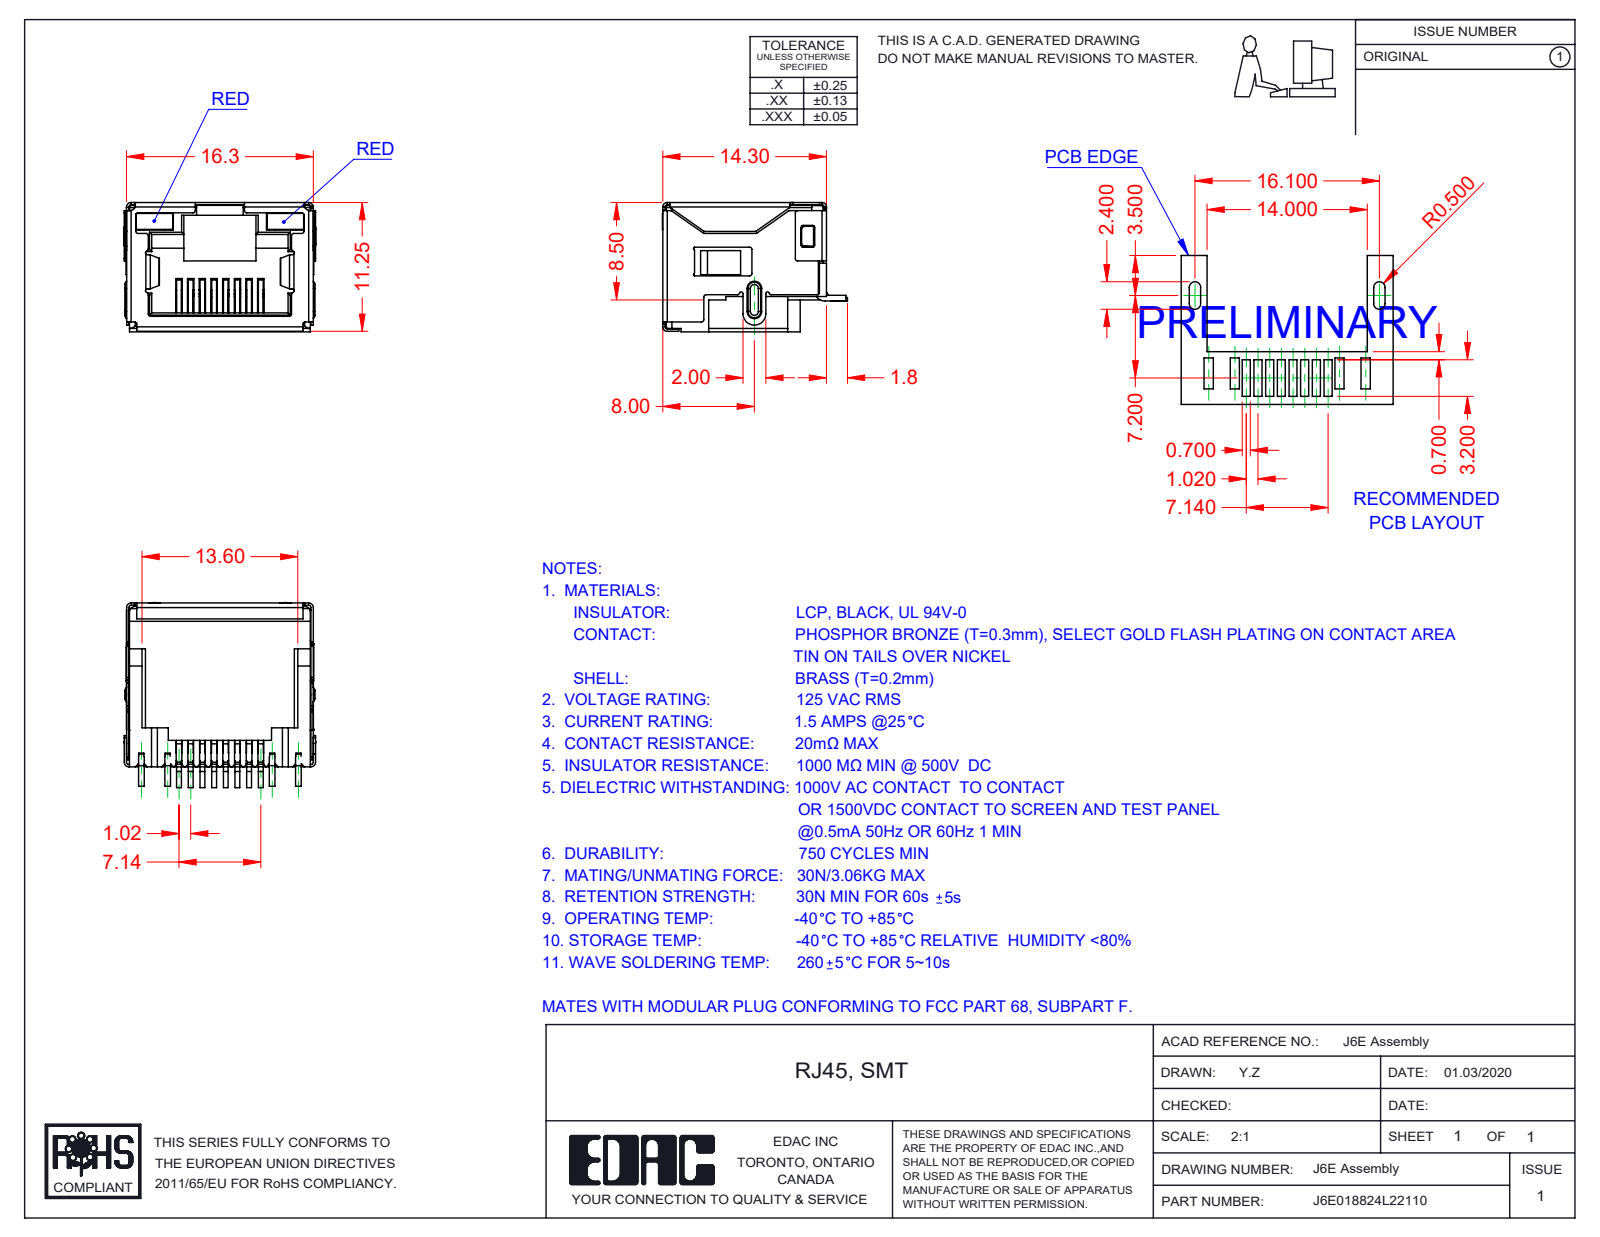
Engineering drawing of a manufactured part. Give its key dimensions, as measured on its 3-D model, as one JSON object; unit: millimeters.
{"part_name": "6E Contacts; 6E Insulator_LED; 6E LED RH_2-Red; 6E LED LH_2-Red (+2 more)", "step_written_by": "SolidWorks 2016 (CONFIG_CONTROL_DESIGN)", "units": "millimeters", "bodies": {"solids": 12, "faces": 1496, "planar": 1099, "cylindrical": 347, "other": 50}, "overall_size": [16.75, 16.15, 11.3], "volume_mm3": 1109, "surface_area_mm2": 4045, "partial_cylinders_radius": [[0.2, 82], [0.25, 17], [0.4, 13], [0.5, 13], [0.1, 10], [0.15, 7], [0.3, 4], [1, 3]], "face_to_face_distances": [11.05, 16.05, 16.1, 15.85, 11.1, 11.3, 2.4, 0.7, 9.85, 0.49]}
